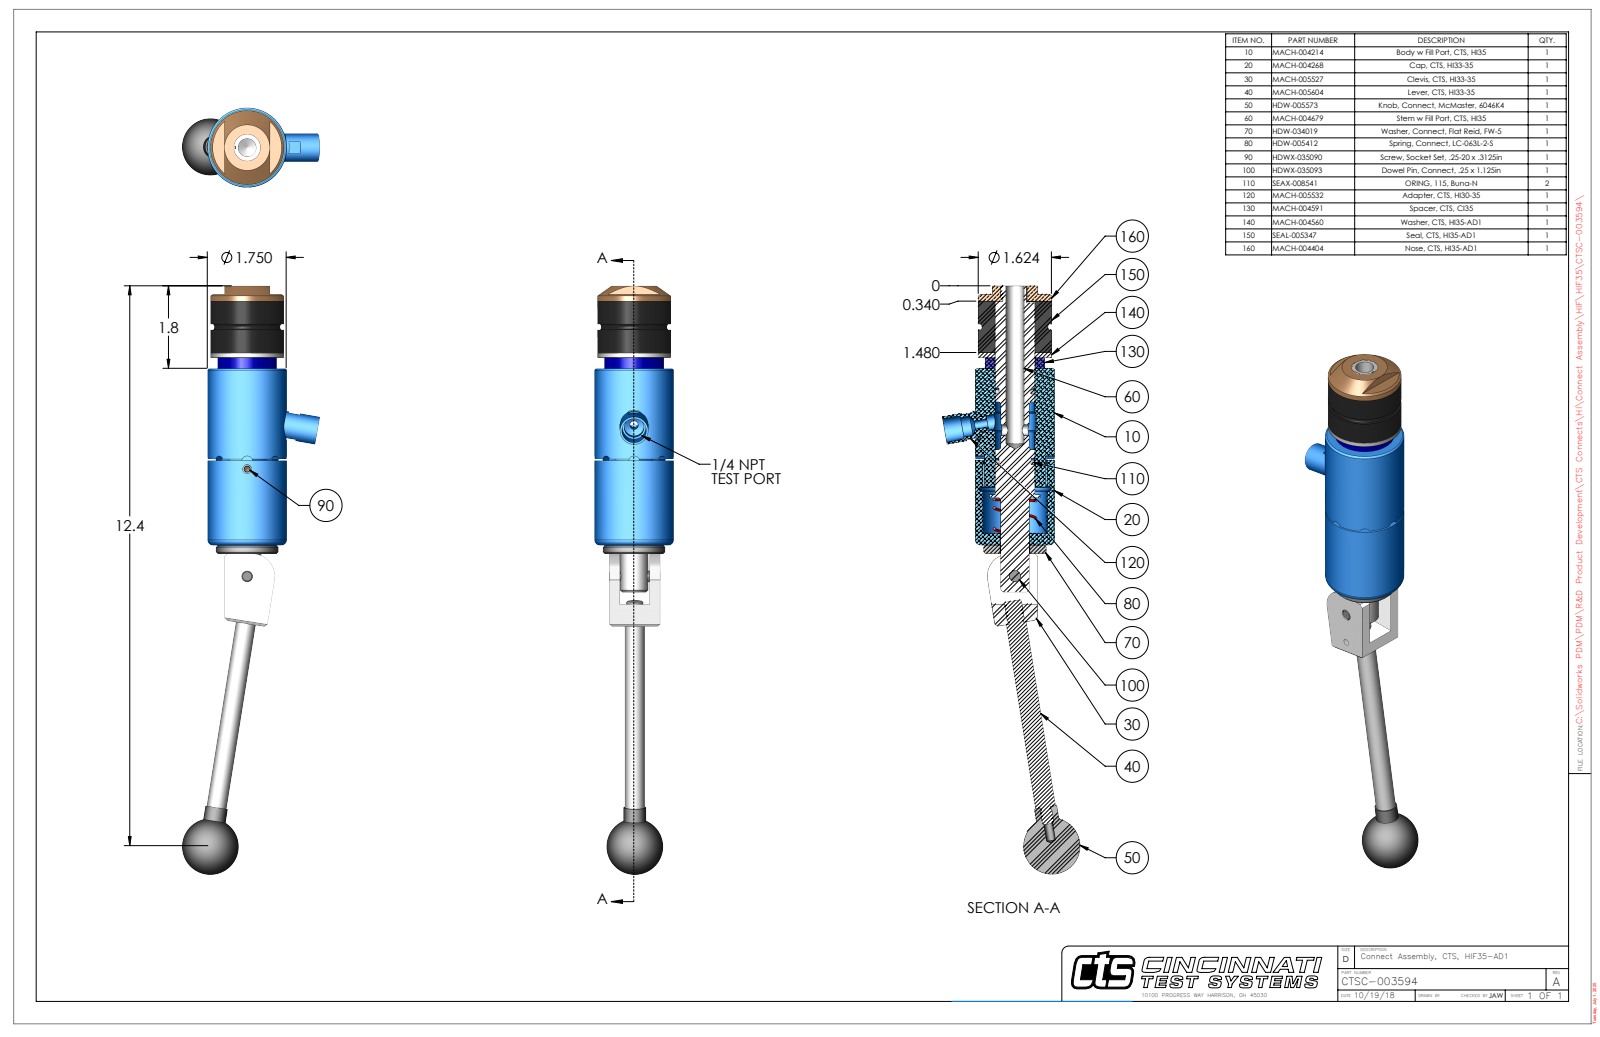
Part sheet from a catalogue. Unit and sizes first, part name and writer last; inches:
Units: inches
Overall size (bounding box): 13.042 × 3.043 × 1.75
Round holes (diameter × count): ⌀0.201 ×2, ⌀0.15 ×1, ⌀0.187 ×1, ⌀0.249 ×1, ⌀0.25 ×1, ⌀0.251 ×1, ⌀0.313 ×1, ⌀0.406 ×1, ⌀0.438 ×1, ⌀0.531 ×1, ⌀0.635 ×1, ⌀0.656 ×1
Round bosses / shafts (diameter × count): ⌀0.25 ×2, ⌀1.75 ×1, ⌀1.624 ×1, ⌀1.38 ×1, ⌀1.312 ×1, ⌀0.869 ×1, ⌀0.625 ×1, ⌀0.62 ×1
Partial cylindrical surfaces — rounded edges, fillets, slot ends (radius × count): R0.125 ×4, R0.029 ×2, R0.166 ×1, R0.246 ×1, R0.33 ×1, R0.5 ×1, R0.695 ×1, R0.818 ×1
Main face-to-face distances: 1.14, 5.405, 4.265, 1.49, 0.35, 3.915, 1.25, 0.11, 0.24, 4.155
Hole centre spacings: 0.74, 2.376, 3.116
Volume: 15.62 in³ · Surface area: 95.54 in²
Bodies: 11 solids, 298 faces (109 planar, 122 cylindrical, 67 other)
Part name (STEP PRODUCT): CTSC-003594
STEP written by: SolidWorks 2023 (AUTOMOTIVE_DESIGN)
